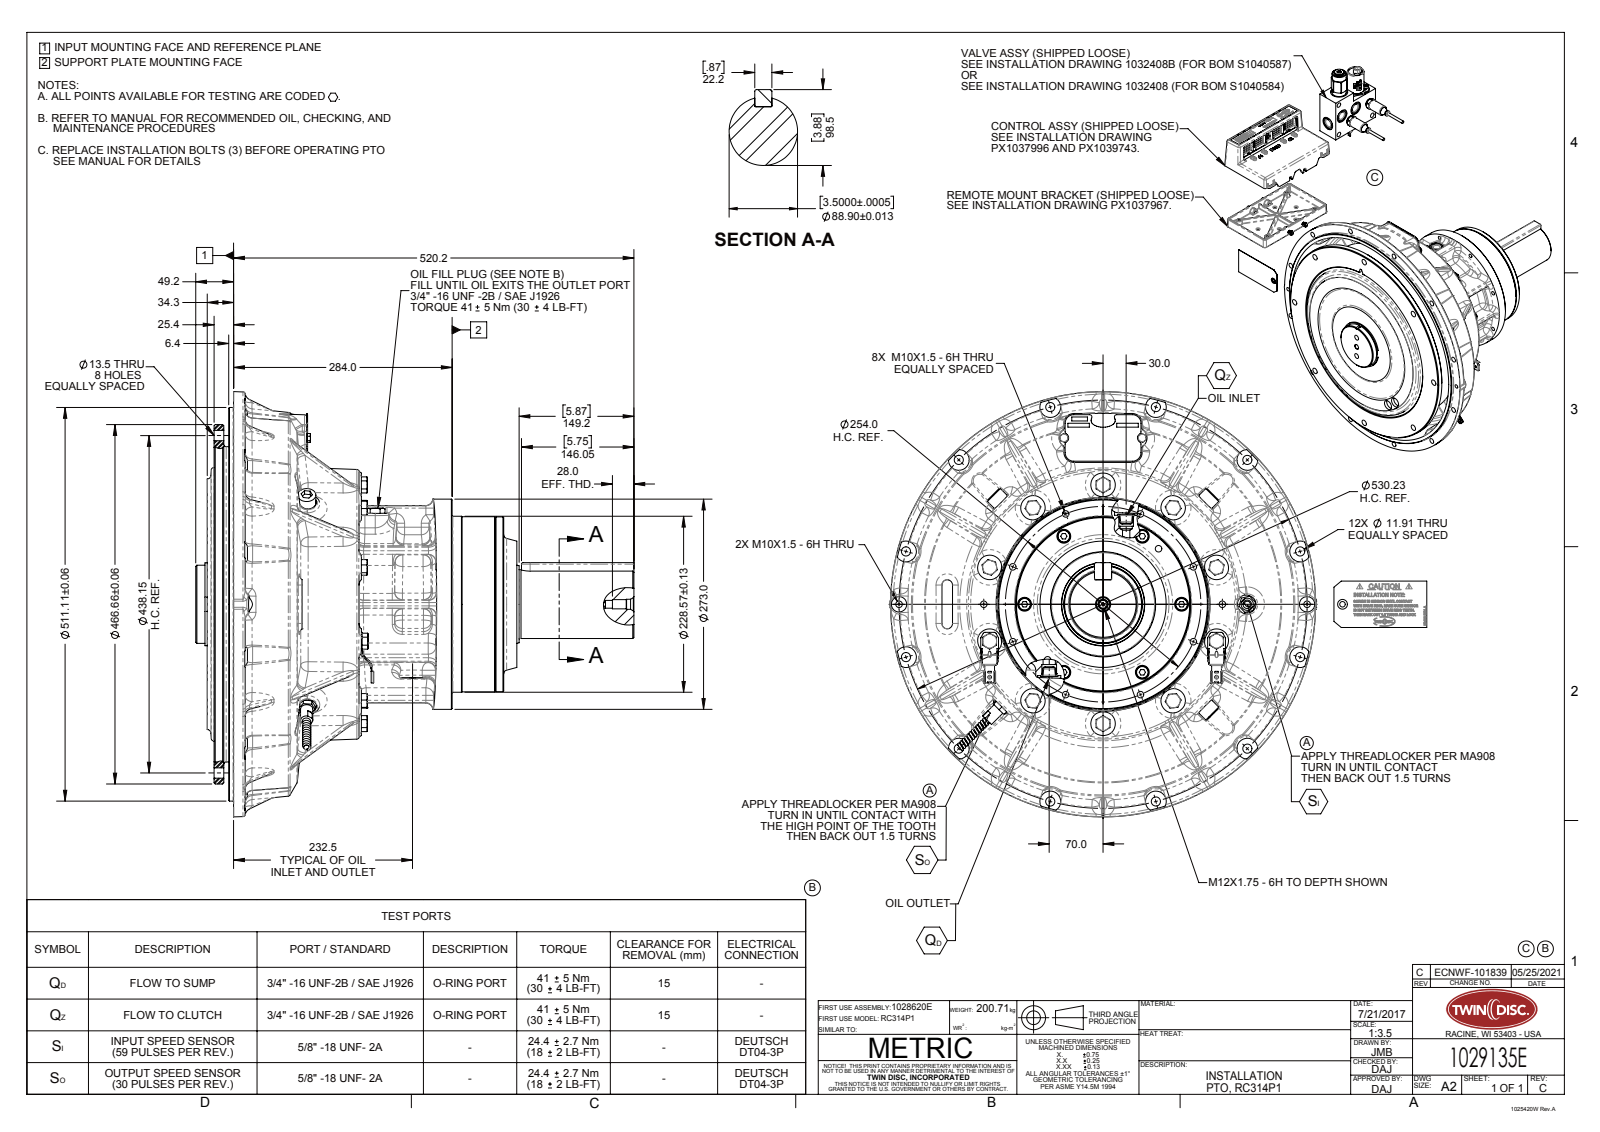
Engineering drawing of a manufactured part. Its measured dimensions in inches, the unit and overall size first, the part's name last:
Units: inches
Overall size (bounding box): 22.417 × 21.813 × 21.744
Round holes (diameter × count): ⌀0.335 ×14, ⌀0.469 ×12, ⌀0.531 ×8, ⌀0.709 ×6, ⌀0.472 ×3, ⌀1.188 ×3, ⌀0.187 ×2, ⌀0.75 ×2, ⌀0.787 ×2, ⌀0.875 ×2, ⌀0.425 ×1, ⌀0.512 ×1
Round bosses / shafts (diameter × count): ⌀0.63 ×4, ⌀0.625 ×2, ⌀0.315 ×2, ⌀20.123 ×1, ⌀18.373 ×1, ⌀10.866 ×1, ⌀10.748 ×1, ⌀8.999 ×1
Partial cylindrical surfaces — rounded edges, fillets, slot ends (radius × count): R0.394 ×93, R0.118 ×63, R0.531 ×12, R0.06 ×10, R0.01 ×5, R0.5 ×5, R0.05 ×3, R0.09 ×3
Main face-to-face distances: 0.748, 1, 0.252, 0.602, 1.35, 0.35, 1.291, 0.543, 0.291, 0.059
Hole centre spacings: 8.148, 4.439, 13.382, 4.016, 11.506, 2.006, 3.827, 5
Bodies: 0 solids, 1719 faces (391 planar, 343 cylindrical, 985 other)
Part name (STEP PRODUCT): 1029135E
STEP written by: SolidWorks 2019 (AUTOMOTIVE_DESIGN)
